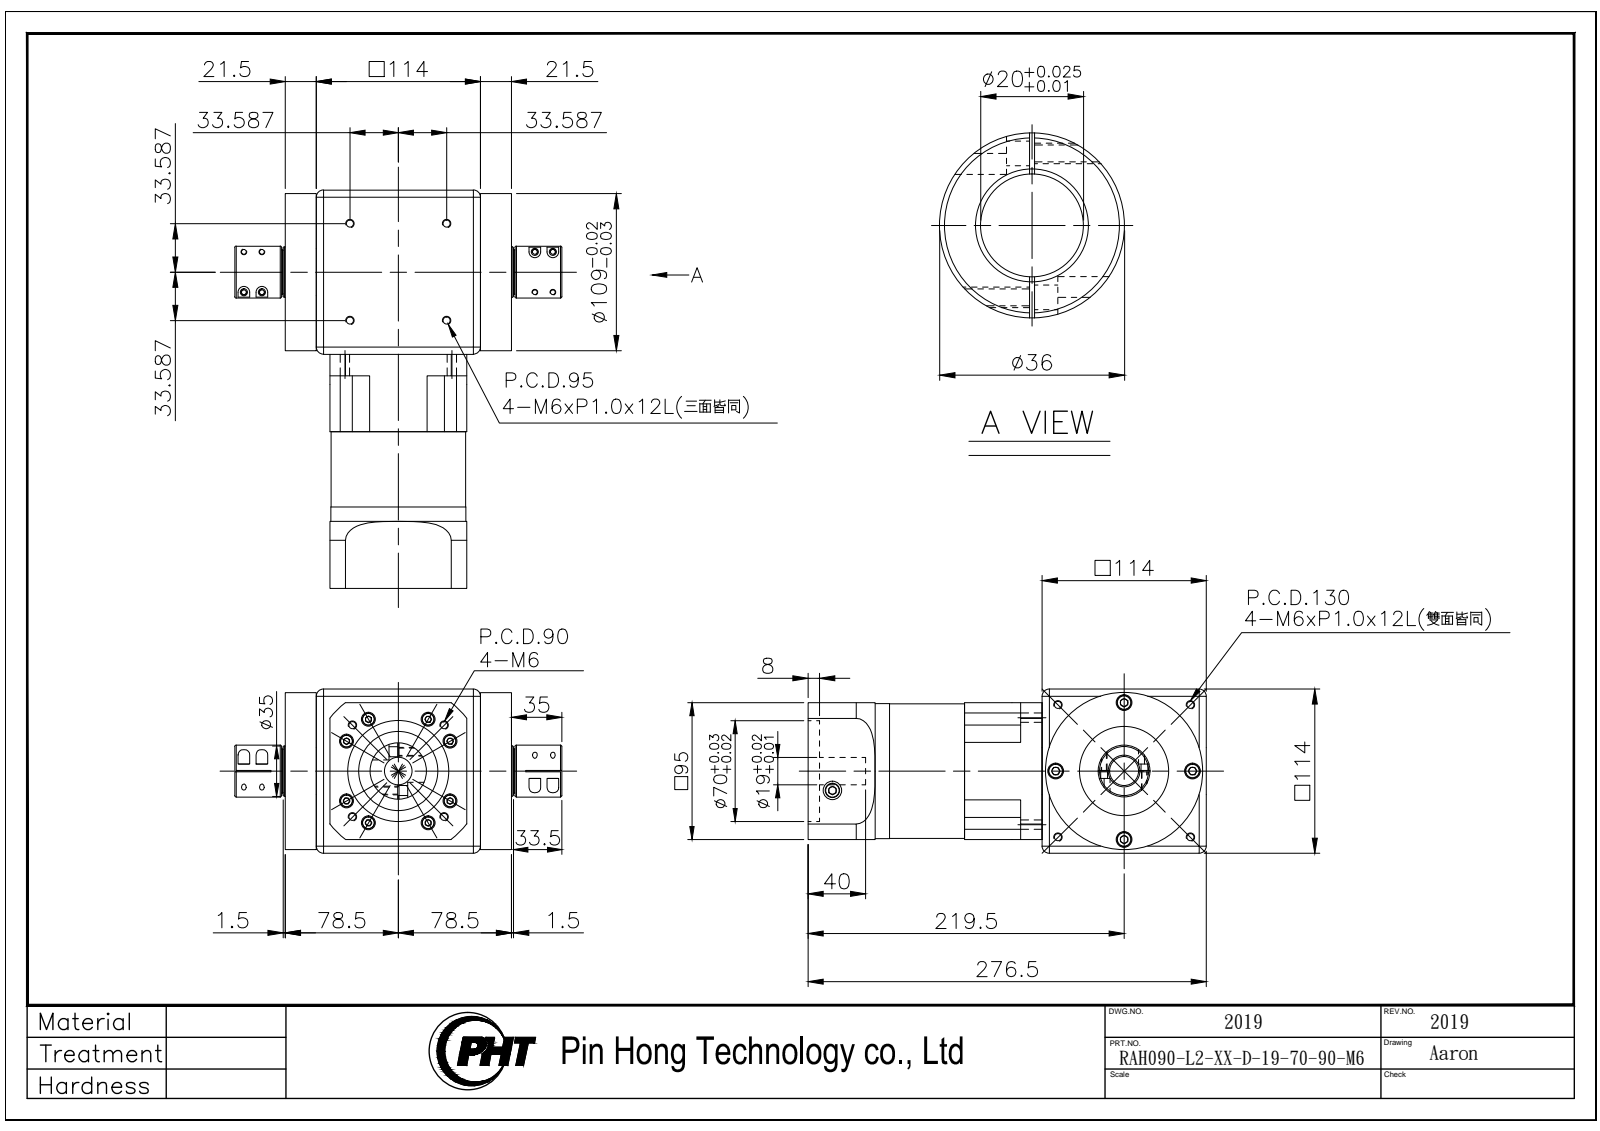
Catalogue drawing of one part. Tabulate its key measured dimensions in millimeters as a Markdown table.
| quantity | value |
| --- | --- |
| part name | RAH090-L2-XX-D-19-70-90-M6_2019 |
| STEP written by | SolidWorks 2016 (AUTOMOTIVE_DESIGN) |
| units | millimeters |
| bodies | 2 solids, 1019 faces (510 planar, 336 cylindrical, 173 other) |
| overall size | 276.5 × 227 × 114 |
| volume | 2 993 000 mm³ |
| surface area | 241 583 mm² |
| round holes (diameter × count) | 5 × 16, 5.2 × 8, 6 × 8, 9.5 × 8, 6.6 × 4, 6.8 × 4, 11 × 4, 12.7 × 2, 19 × 1, 20 × 1, 27 × 1, 28 × 1 |
| round bosses / shafts (diameter × count) | 8.5 × 16, 10 × 8, 9.2 × 8, 5 × 8, 109 × 1, 93.8 × 1, 93.5 × 1, 80 × 1 |
| partial cylindrical surfaces (radius × count) | 4.75 × 8, 2.55 × 4, 6 × 4, 52 × 1, 60 × 1, 79.1 × 1 |
| main face-to-face distances | 114, 104.5, 9.5, 31, 95, 126, 135.5, 21.5, 157, 3 |
| hole center spacings | 41.5, 67.18, 11.81, 13.05, 16.41, 45.99, 47.5, 52.73 |
